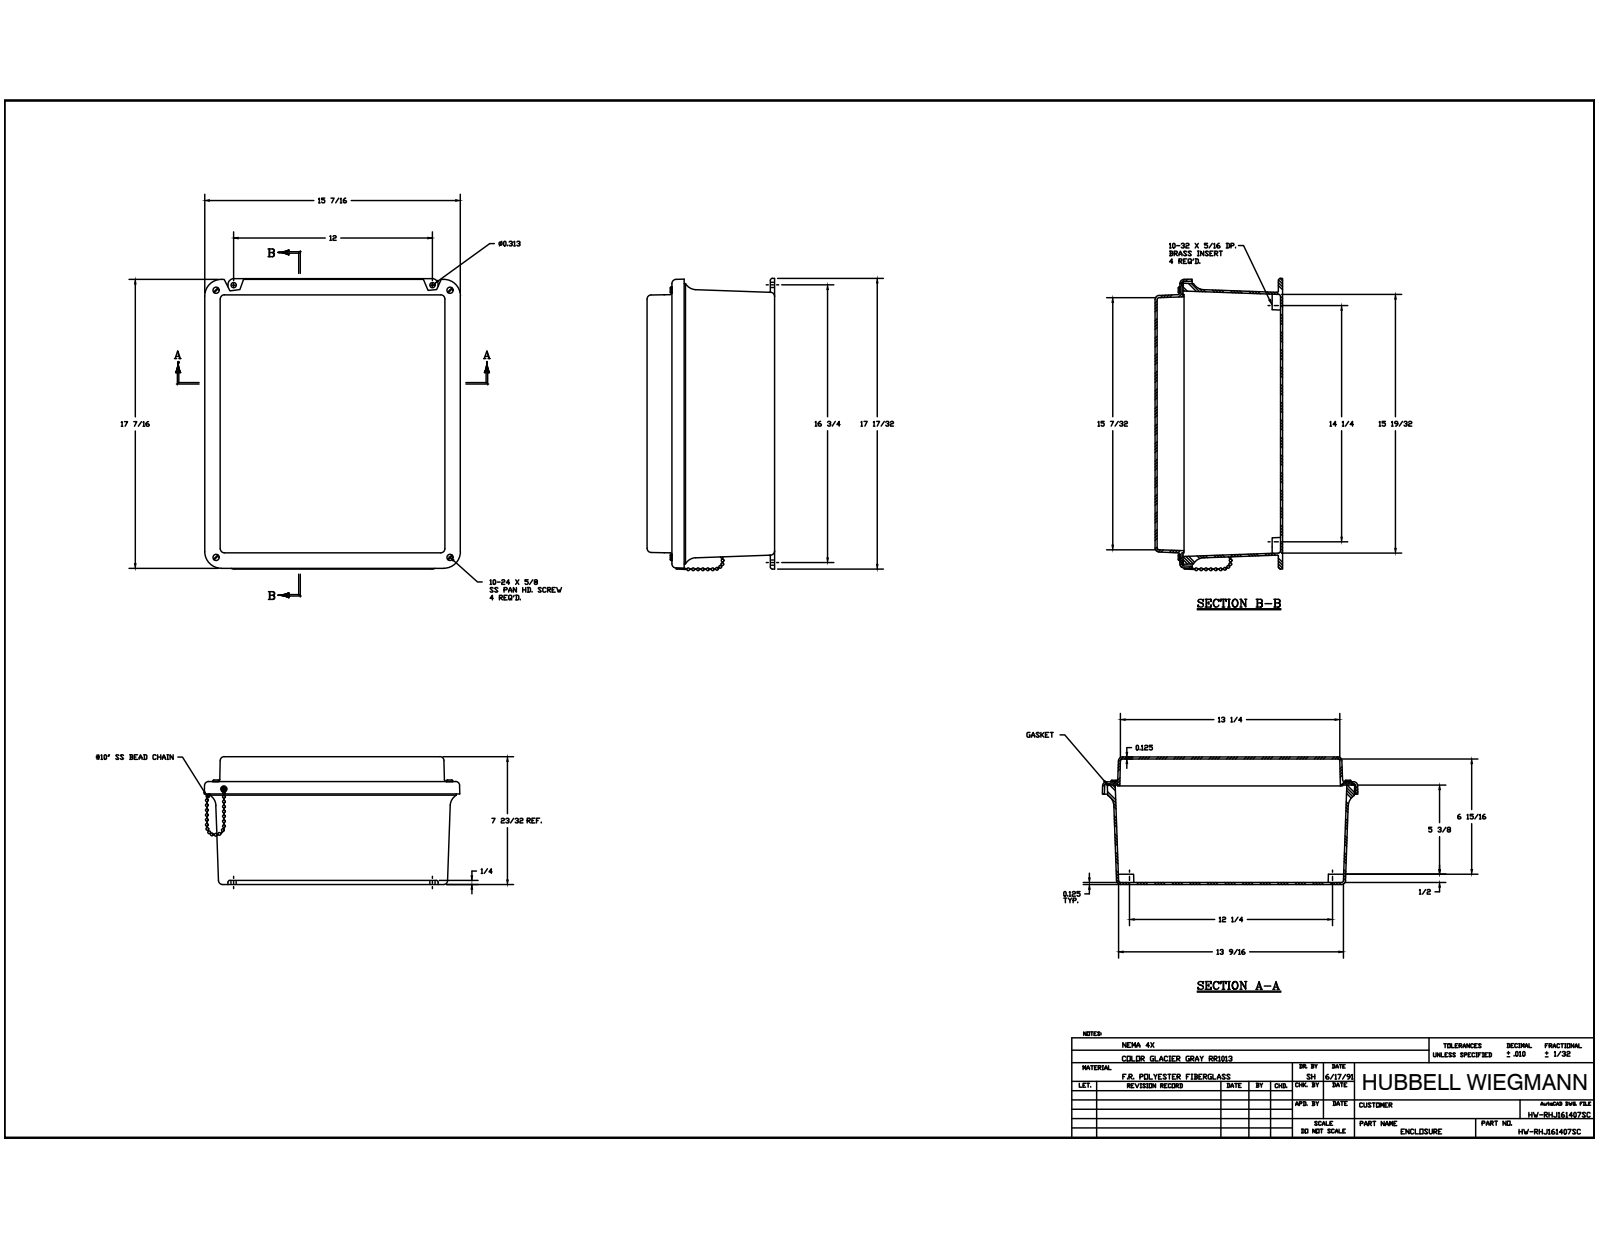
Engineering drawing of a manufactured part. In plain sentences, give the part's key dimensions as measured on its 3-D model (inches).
The part is named "J1614W_3; RMINS45821P_107; RMINS45821P_108; RMINS45821P_109 (+8 more)". Its 3-D file was written by "Autodesk Inventor 2014 (AUTOMOTIVE_DESIGN)". It is 21 solids with 925 faces: 214 planar, 307 cylindrical and 404 other. Overall it measures 18.091 by 15.742 by 7.684 inches. Its volume is 146.1 cubic inches and its surface area 2 060 square inches. Round holes: 8 of diameter 0.152, 6 of diameter 0.14, 4 of diameter 0.145, 4 of diameter 0.156, 4 of diameter 0.218, 2 of diameter 0.187, 1 of diameter 0.126. Round bosses or shafts: 8 of diameter 0.27, 4 of diameter 0.19, 4 of diameter 0.156, 2 of diameter 0.375, 2 of diameter 0.25, 2 of diameter 0.125, 1 of diameter 0.283. Partial cylindrical surfaces (rounded edges, fillets, slot ends): 20 of radius 0.031, 20 of radius 0.125, 20 of radius 0.25, 4 of radius 0.2, 4 of radius 0.297, 4 of radius 0.375, 4 of radius 0.75, 2 of radius 0.01. The main face-to-face distances are 0.125, 0.125, 7.434, 7.684, 7.559, 7.559, 1.502, 5.932, 6.057, 1.627. The hole center spacings are 1.321, 13.22, 15.209, 20.108, 3.75, 7.5, 12.25, 14.125.
